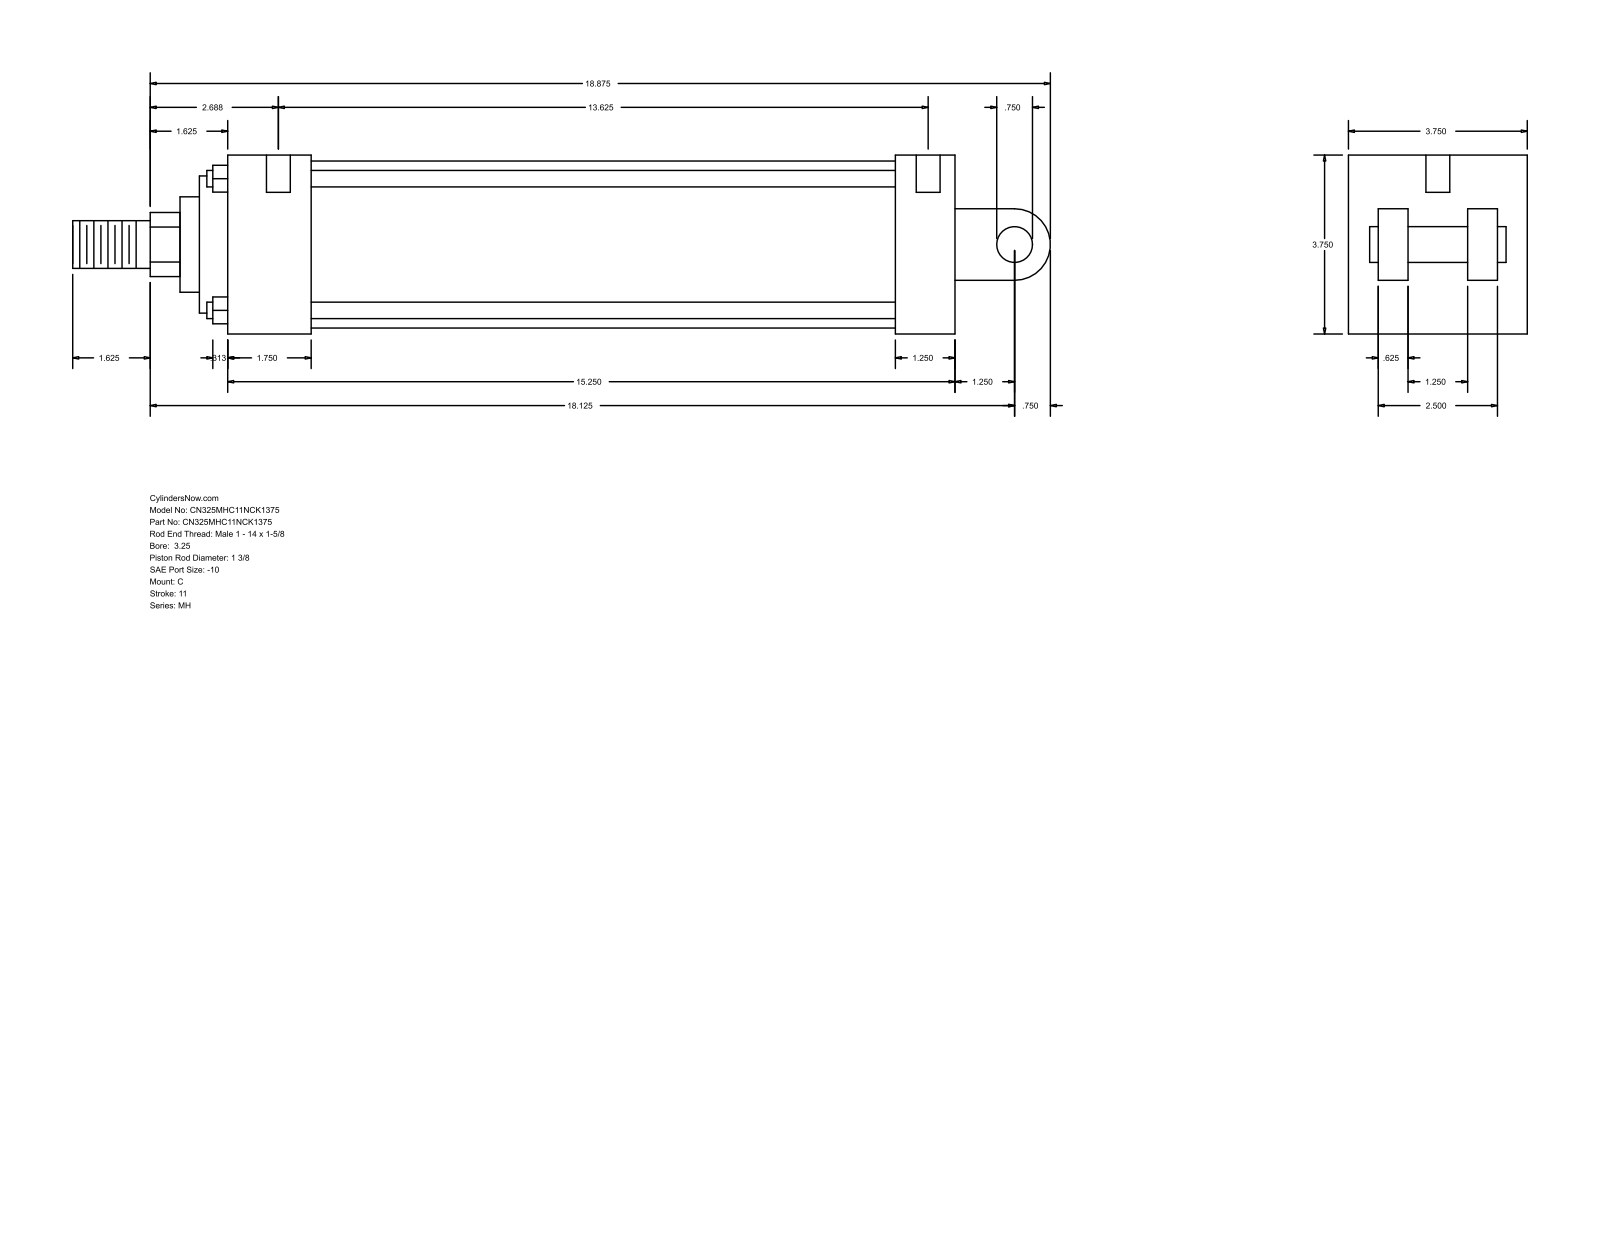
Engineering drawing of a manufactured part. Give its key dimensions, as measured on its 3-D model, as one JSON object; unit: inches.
{"part_name": "MH_C__0325_1.375", "step_written_by": "GSSL Pune (CONFIG_CONTROL_DESIGN)", "units": "inches", "bodies": {"solids": 0, "faces": 101, "planar": 71, "cylindrical": 30, "other": 0}, "overall_size": [20.5, 3.75, 3.75], "round_holes": [[0.219, 4], [0.5, 2]], "round_bosses_or_shafts": [[0.345, 4], [3.5, 1], [2.875, 1], [2, 1], [1.375, 1], [1, 1], [0.75, 1]], "partial_cylinders_radius": [[0.672, 1], [0.75, 1]], "face_to_face_distances": [3.75, 0.625, 1.25, 2.5, 15.25, 3.125, 1.875, 1.75, 14, 12.25], "hole_center_spacings": [13.875, 0.063, 0.187, 13.625, 13.688, 13.813]}
